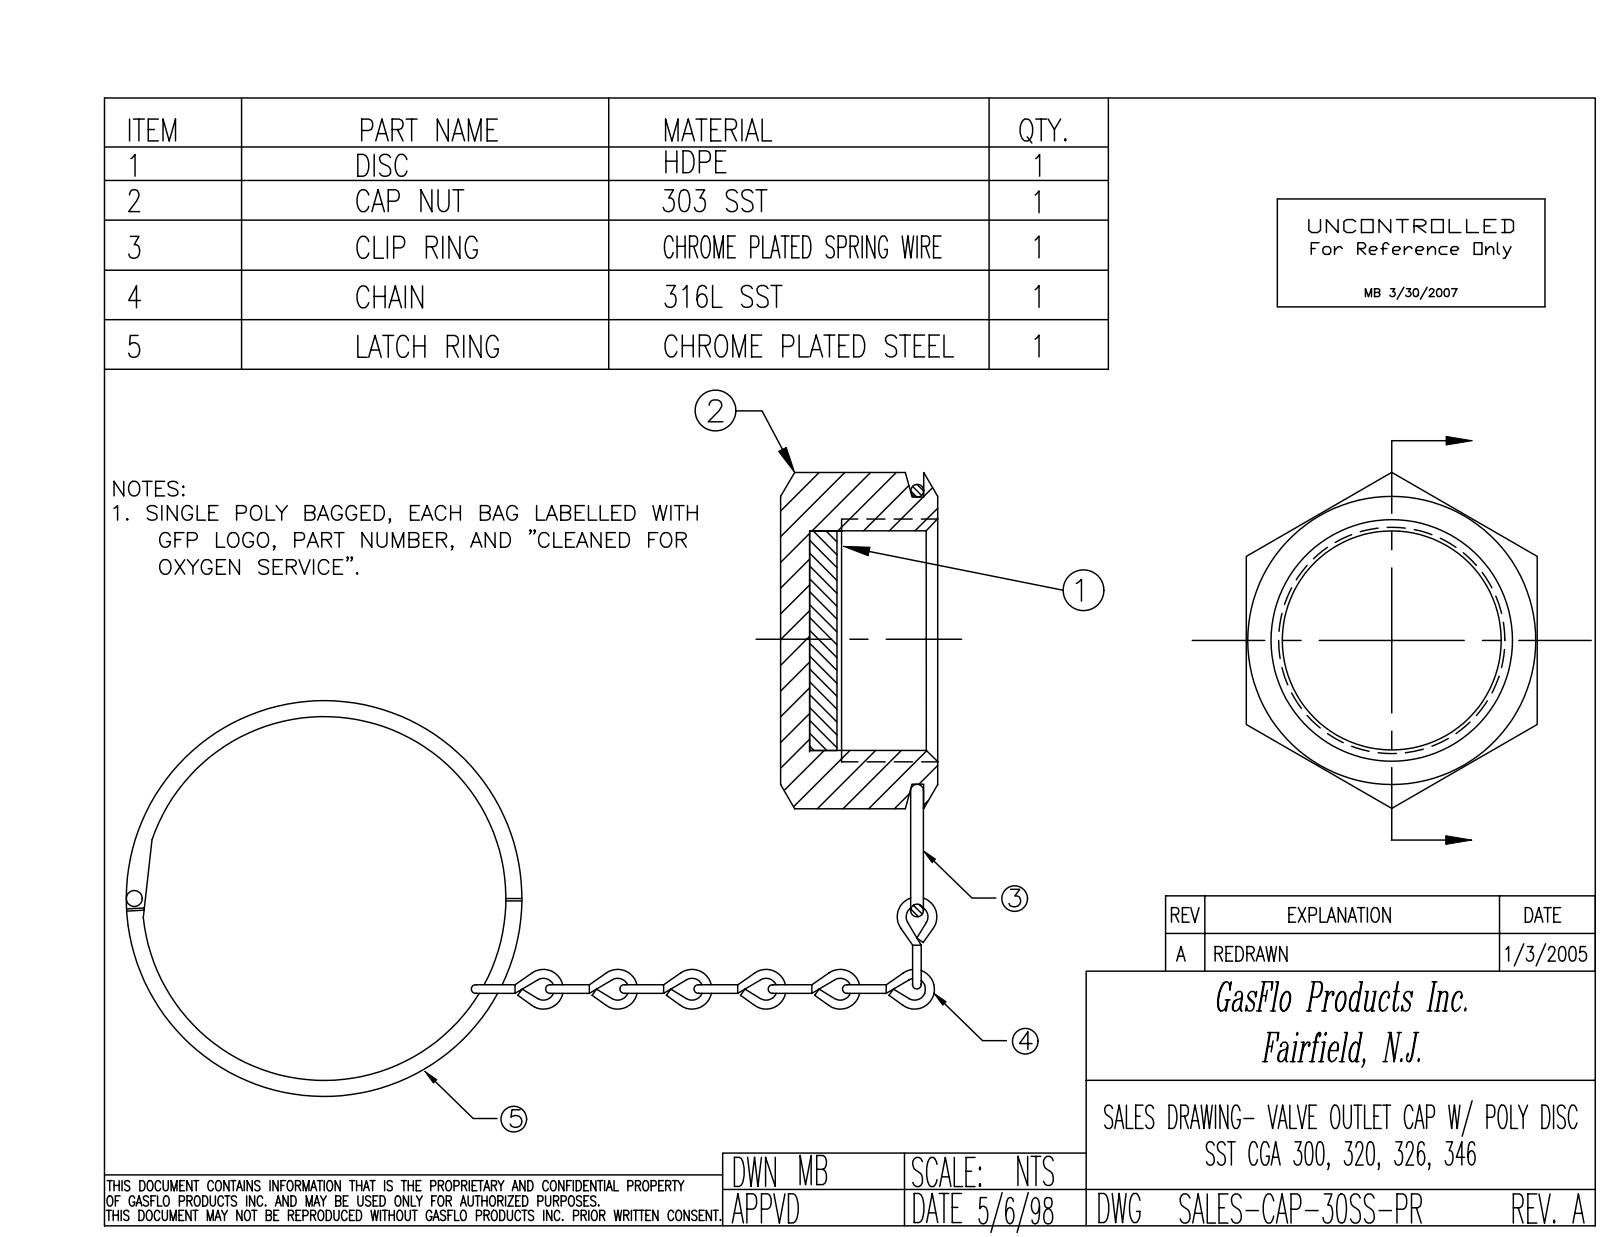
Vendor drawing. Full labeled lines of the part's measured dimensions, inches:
Part name (STEP PRODUCT): ASY-000291; ASY-000211_One Link Bent; CAP-30SS-PR; PRT-002239_STAINLESS (+5 more)
STEP written by: SolidWorks 2018 (CONFIG_CONTROL_DESIGN)
Units: inches
Bodies: 13 solids, 306 faces (56 planar, 117 cylindrical, 133 other)
Overall size (bounding box): 4.217 × 1.755 × 1.233
Volume: 0.376 in³ · Surface area: 10.97 in²
Round holes (diameter × count): ⌀0.063 ×1, ⌀0.757 ×1
Round bosses / shafts (diameter × count): ⌀0.063 ×31, ⌀0.993 ×1, ⌀0.757 ×1, ⌀0.1 ×1
Partial cylindrical surfaces — rounded edges, fillets, slot ends (radius × count): R0.005 ×24, R0.25 ×4, R0.01 ×2
Main face-to-face distances: 0.1, 1, 0.194, 0.094, 1, 0.54, 0.44, 0.346, 0.478, 0.378
